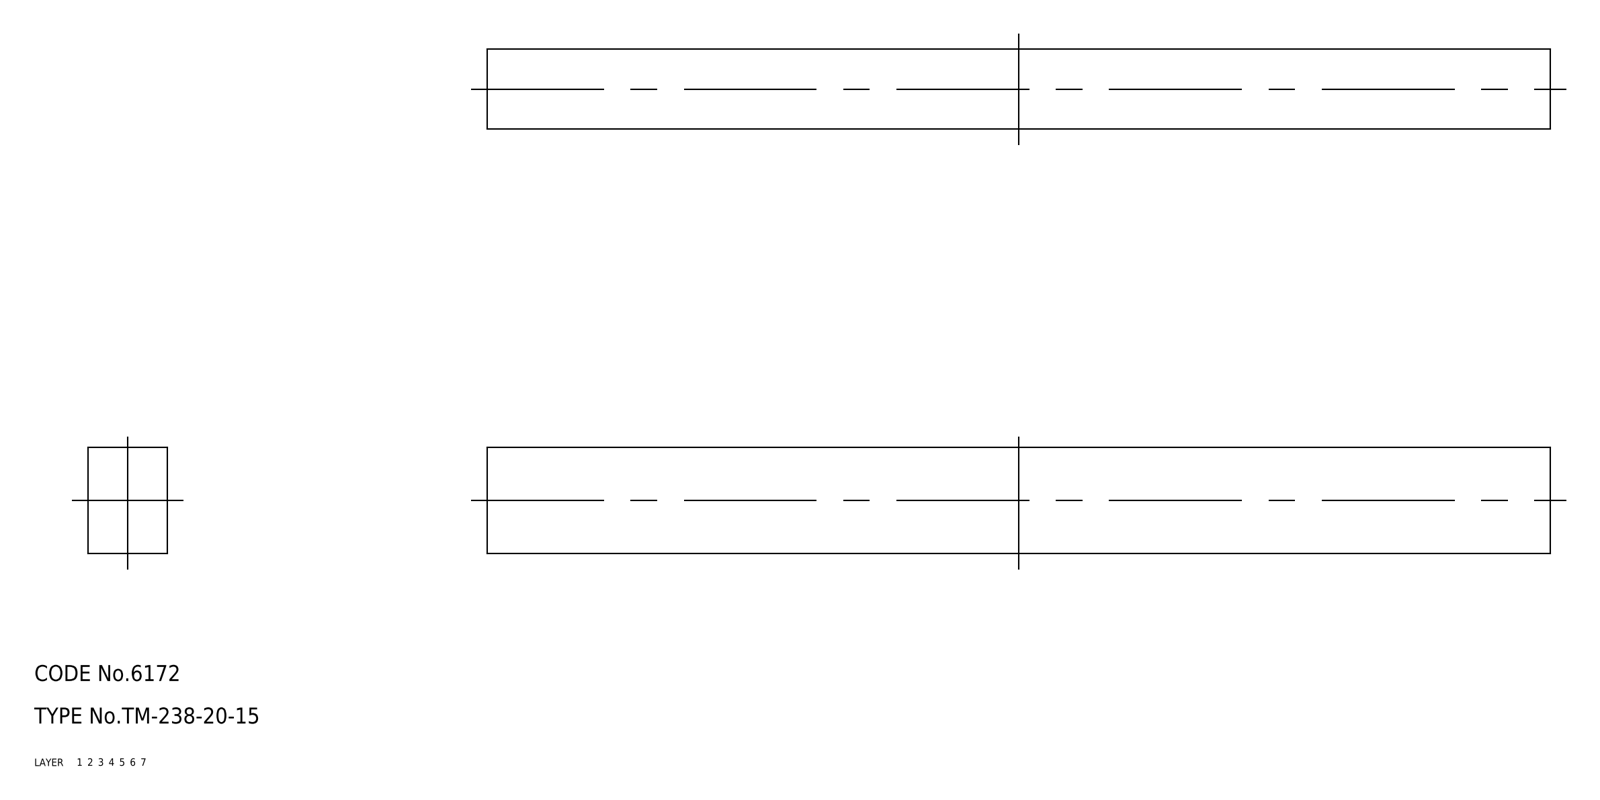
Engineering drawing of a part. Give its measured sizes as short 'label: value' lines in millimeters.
name: rubber foam
written by: CADfix (AUTOMOTIVE_DESIGN)
unit: mm
bodies: 1 solid, 6 faces (0 planar, 0 cylindrical, 6 other)
size: 200 × 20 × 15
volume: 60 000 mm³; area: 14 600 mm²
